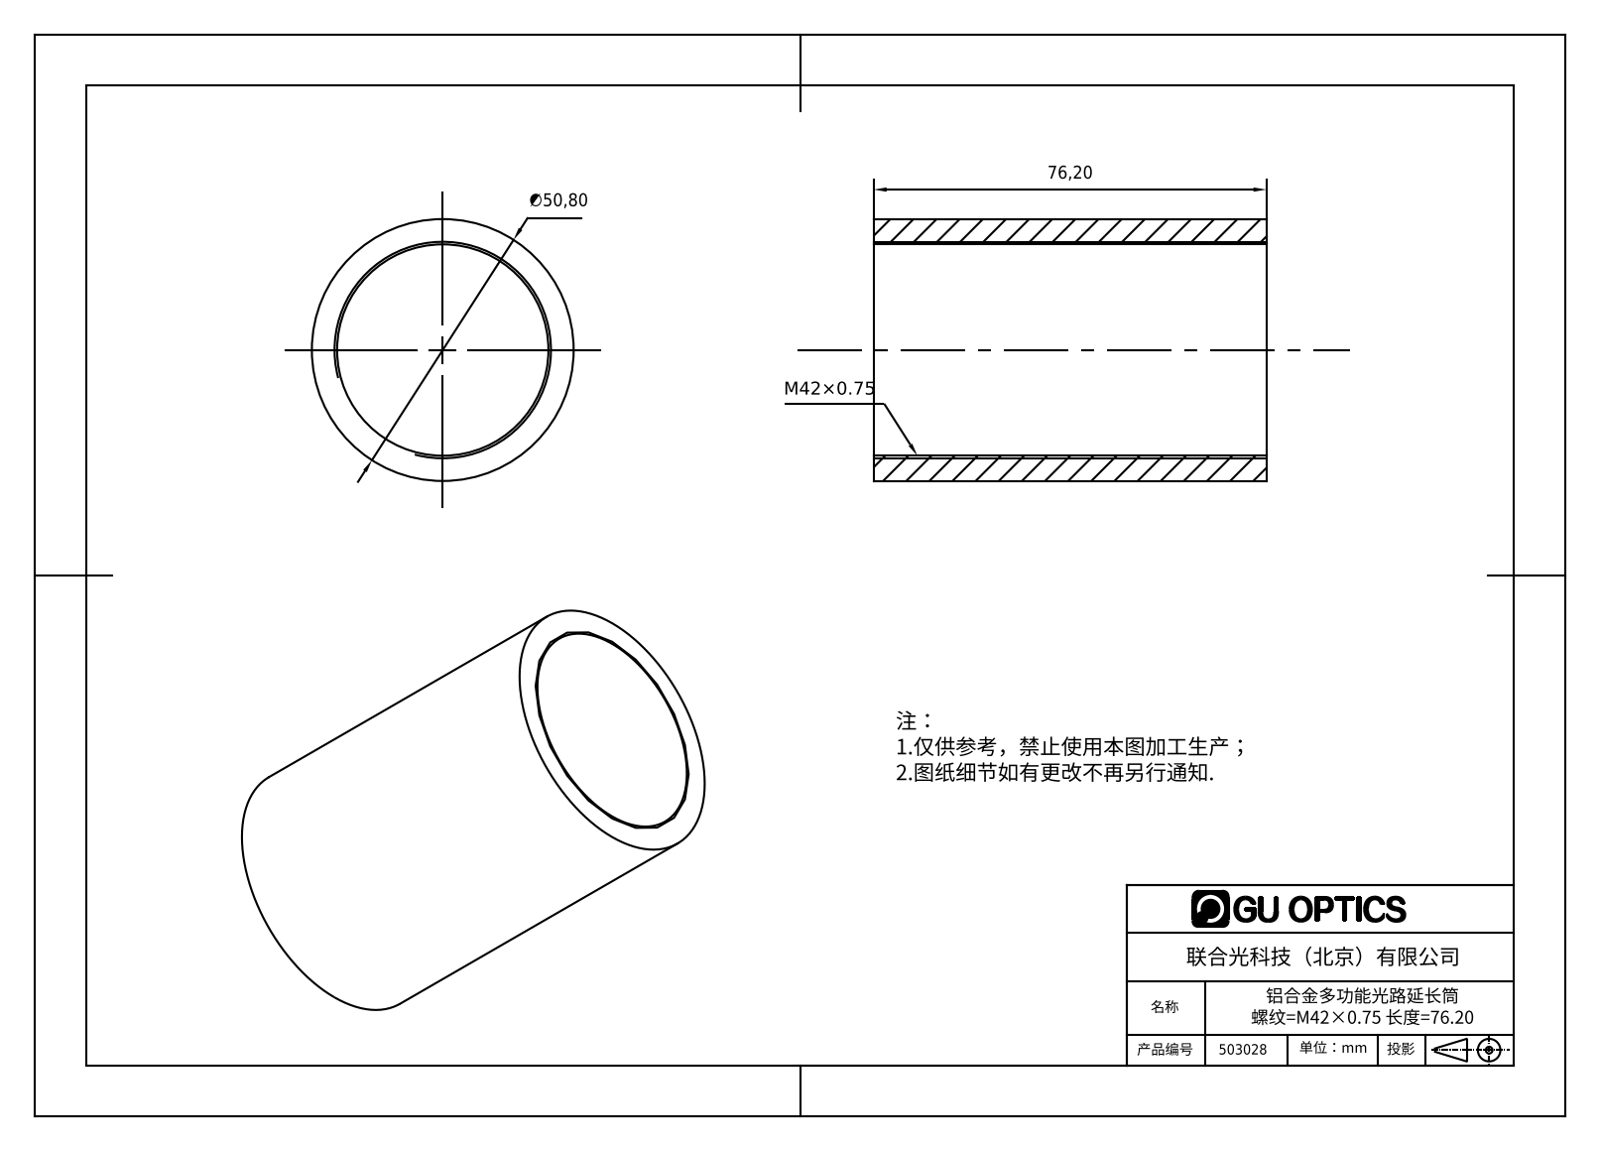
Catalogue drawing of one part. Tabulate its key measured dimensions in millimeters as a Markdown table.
| quantity | value |
| --- | --- |
| part name | 503028 |
| STEP written by | SolidWorks 2016 (AUTOMOTIVE_DESIGN) |
| units | millimeters |
| bodies | 1 solid, 6 faces (2 planar, 4 cylindrical, 0 other) |
| overall size | 76.2 × 50.8 × 50.8 |
| volume | 53 841 mm³ |
| surface area | 23 389 mm² |
| round holes (diameter × count) | 41 × 1 |
| round bosses / shafts (diameter × count) | 50.8 × 1 |
| main face-to-face distances | 76.2 |
